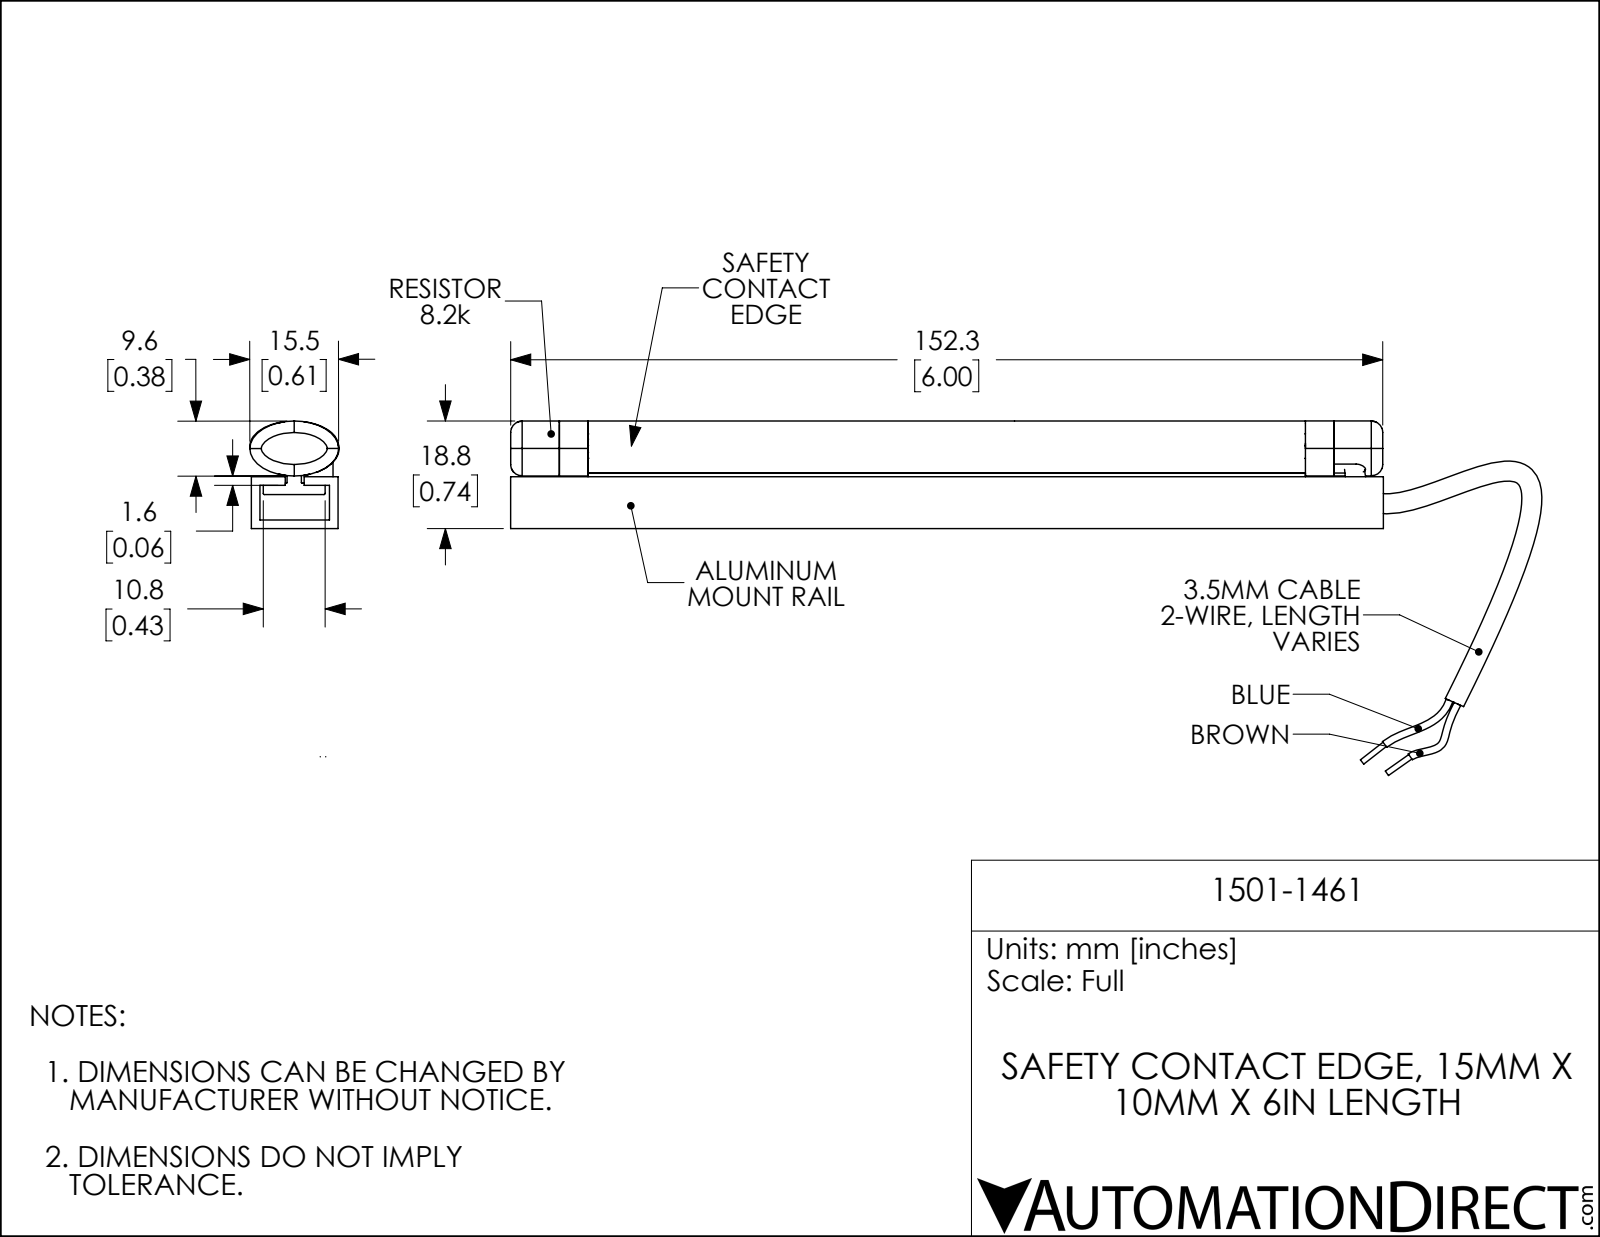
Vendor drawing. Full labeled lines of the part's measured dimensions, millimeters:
Part name (STEP PRODUCT): 1501-1461
STEP written by: SolidWorks 2018 (AUTOMOTIVE_DESIGN)
Units: millimetres
Bodies: 7 solids, 610 faces (129 planar, 154 cylindrical, 327 other)
Overall size (bounding box): 180.1 × 61.9 × 15.6
Volume: 25 090 mm³ · Surface area: 29 050 mm²
Round holes (diameter × count): ⌀1.2 ×4
Round bosses / shafts (diameter × count): ⌀0.9 ×2
Partial cylindrical surfaces — rounded edges, fillets, slot ends (radius × count): R0.1 ×56, R0.4 ×16, R0.3 ×10, R0.2 ×7, R0.5 ×4, R1.5 ×4, R2.5 ×4, R13 ×4
Main face-to-face distances: 1.5, 7.5, 13.6, 9, 15.1, 6, 5.9, 4.4, 1.6, 3.1
Hole centre spacings: 5, 4.9, 5.1
